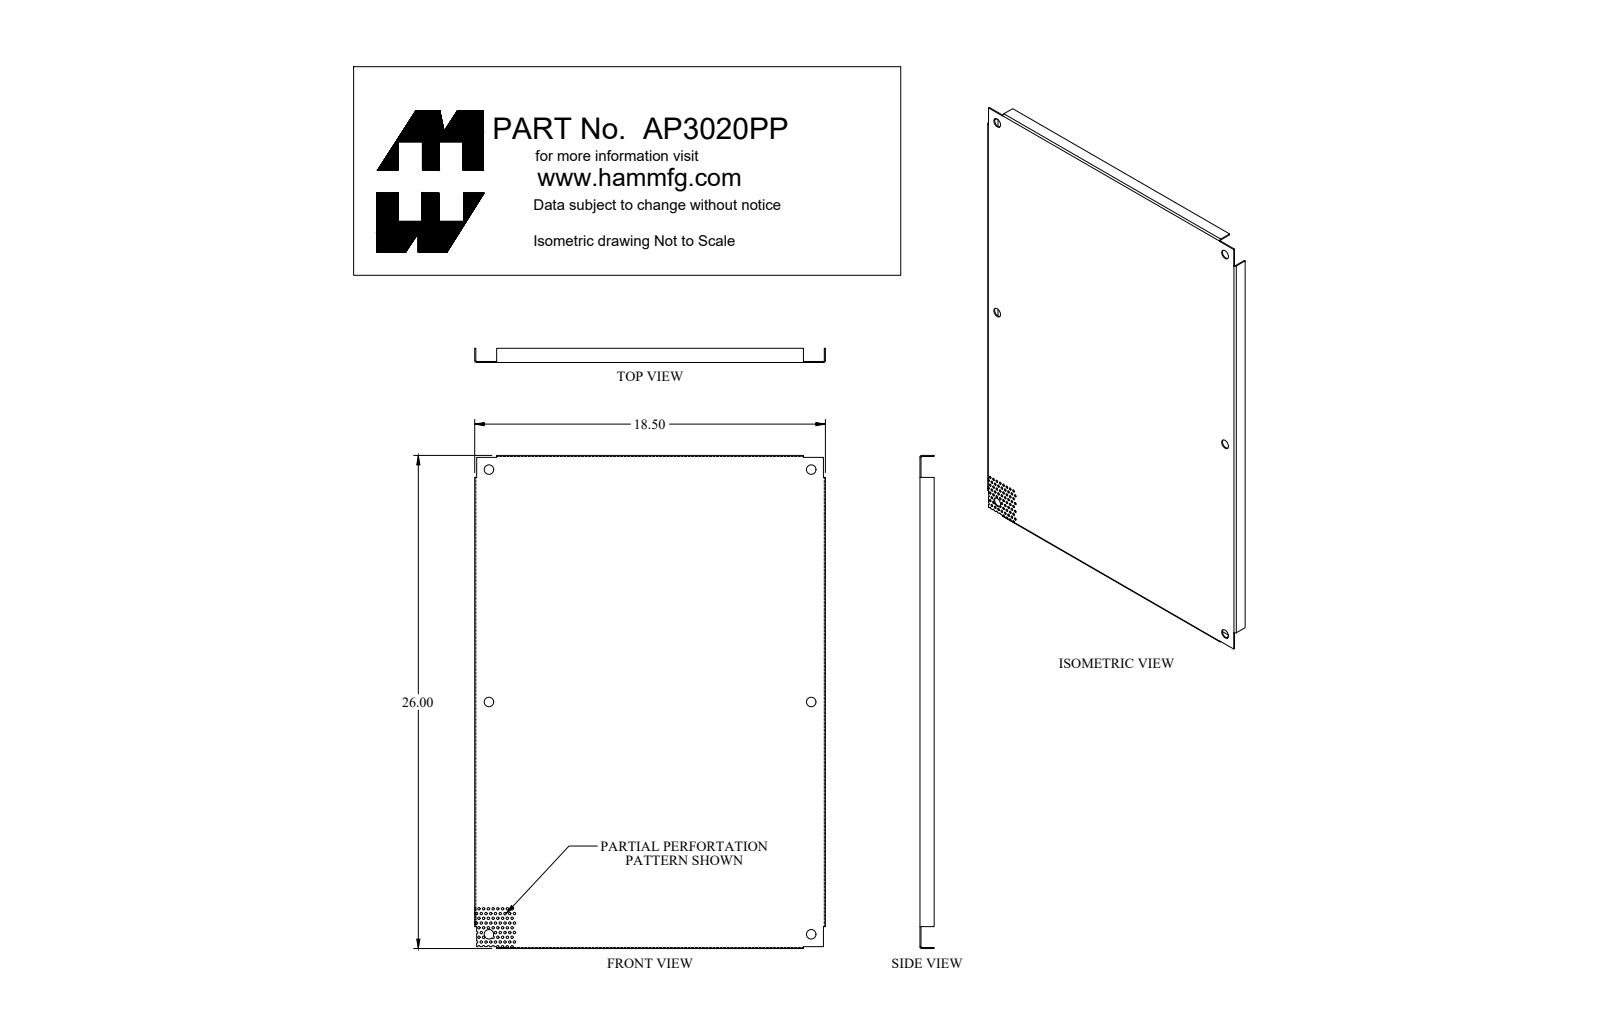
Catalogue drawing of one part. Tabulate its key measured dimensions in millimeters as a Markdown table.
| quantity | value |
| --- | --- |
| part name | AP3020PP_Default |
| STEP written by | SolidWorks 2019 (CONFIG_CONTROL_DESIGN) |
| units | millimeters |
| bodies | 1 solid, 264 faces (43 planar, 213 cylindrical, 8 other) |
| overall size | 660.4 × 469.9 × 19.1 |
| volume | 496 000 mm³ |
| surface area | 690 300 mm² |
| round holes (diameter × count) | 3.2 × 74, 12.7 × 6, 3.2 × 2 |
| partial cylindrical surfaces (radius × count) | 1.6 × 13, 1.6 × 8, 0.7 × 4, 2.2 × 4 |
| main face-to-face distances | 1.4, 468.5, 659, 467, 469.9, 660.4, 657.5, 19.1, 17.6, 2.6 |
| hole center spacings | 7.1, 12.7, 6.4, 14.2, 11.5, 19.3, 17.1, 19.1 |
